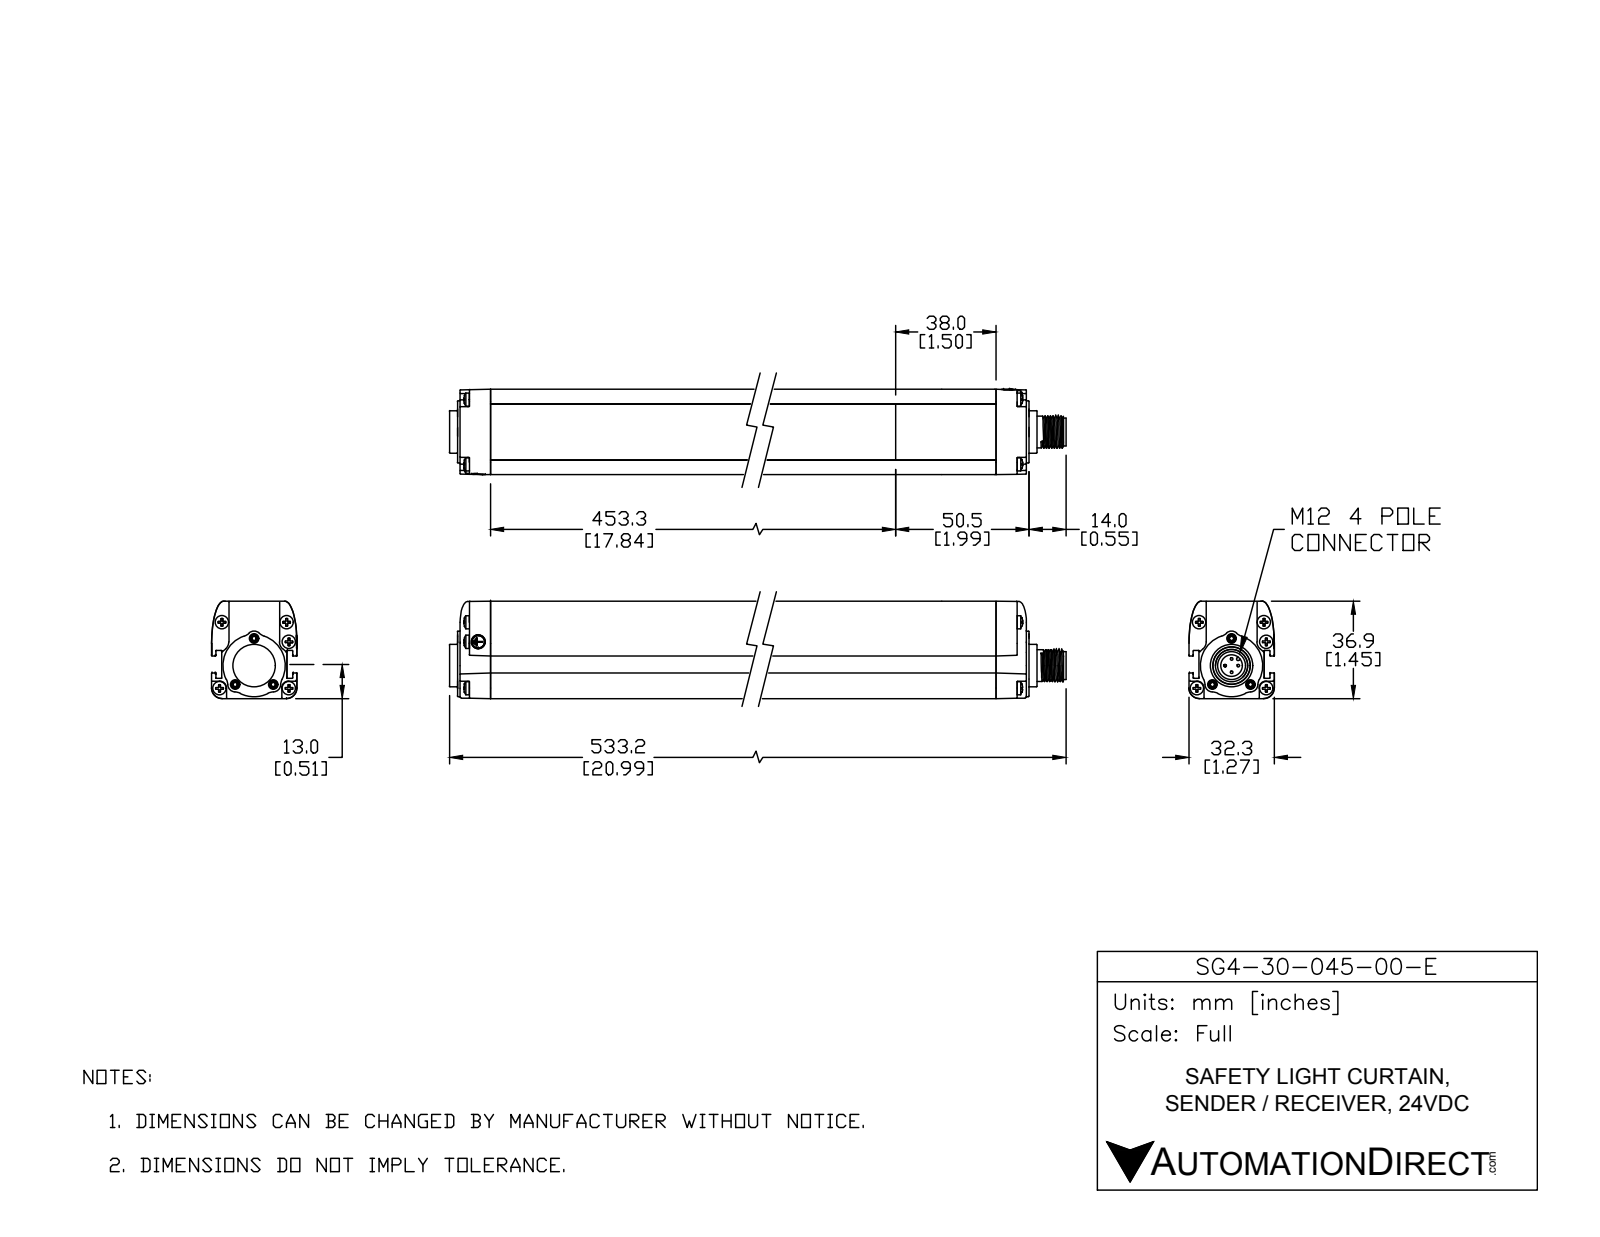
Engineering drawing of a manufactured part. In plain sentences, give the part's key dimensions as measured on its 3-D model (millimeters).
The part is named "SG4-30-045-OO-E". Its 3-D file was written by "SolidWorks 2017 (AUTOMOTIVE_DESIGN)". It is 29 solids with 1674 faces: 410 planar, 591 cylindrical and 673 other. Overall it measures 533.3 by 63 by 52.2 millimeters. Its volume is 546 500 cubic millimeters and its surface area 141 400 square millimeters. Round holes: 6 of diameter 2.7, 6 of diameter 5.3, 4 of diameter 2.1, 4 of diameter 4.2, 4 of diameter 6.6, 3 of diameter 1.5, 3 of diameter 3.6, 1 of diameter 8.2, 1 of diameter 9.6, 1 of diameter 11, 1 of diameter 14.3. Round bosses or shafts: 10 of diameter 5, 4 of diameter 10, 4 of diameter 1, 2 of diameter 4.7, 1 of diameter 16, 1 of diameter 14, 1 of diameter 12, 1 of diameter 10.5. Partial cylindrical surfaces (rounded edges, fillets, slot ends): 148 of radius 0.2, 120 of radius 0.1, 18 of radius 0.2, 18 of radius 2.7, 8 of radius 3, 7 of radius 5, 3 of radius 2.8, 2 of radius 0.4. The main face-to-face distances are 2, 32.3, 3.8, 36.3, 28.5, 34.3, 4, 3, 24.7, 8.5. The hole center spacings are 14.5, 451.3, 10.2, 6.1, 7.4, 13.2, 13.7, 15.7.
